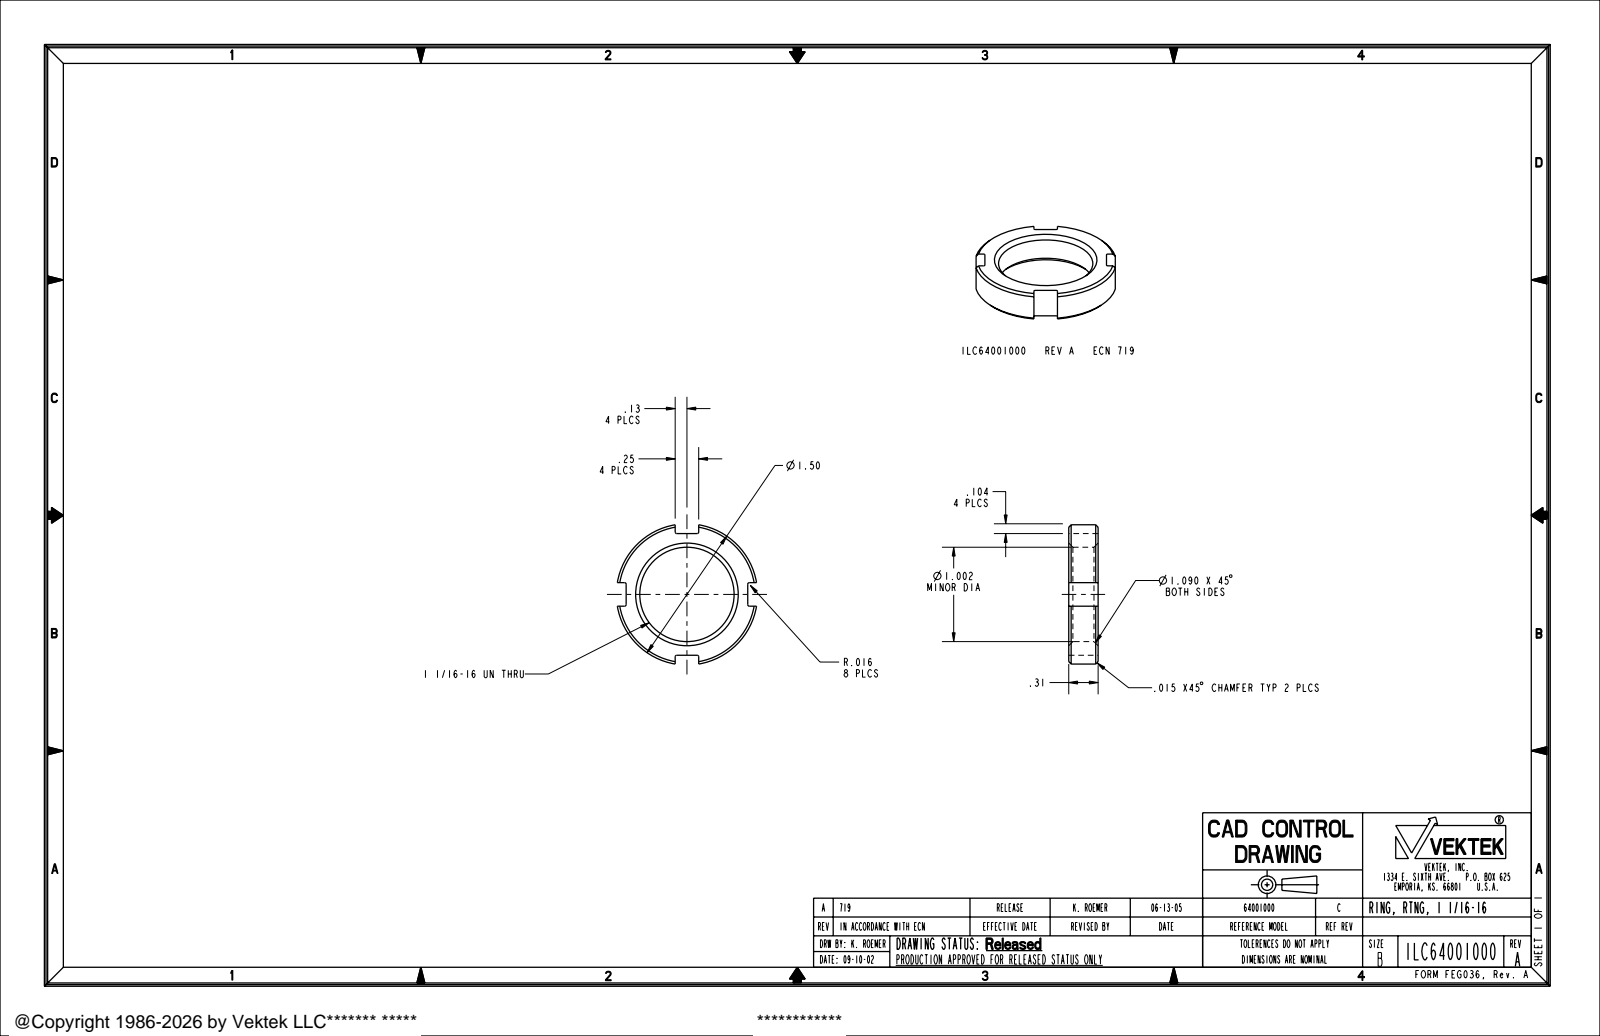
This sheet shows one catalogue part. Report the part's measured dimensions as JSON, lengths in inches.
{"part_name": "ILC64001000", "step_written_by": "PRO/ENGINEER BY PARAMETRIC TECHNOLOGY CORPORATION, 2004290 (AUTOMOTIVE_DESIGN_CC2)", "units": "inches", "bodies": {"solids": 1, "faces": 40, "planar": 14, "cylindrical": 14, "other": 12}, "overall_size": [1.5, 1.5, 0.312], "volume_in3": 0.265, "surface_area_in2": 4.149, "round_holes": [[1.002, 1]], "partial_cylinders_radius": [[0.016, 8], [0.75, 1]], "face_to_face_distances": [0.312, 0.521, 0.771, 1.292, 0.25]}
